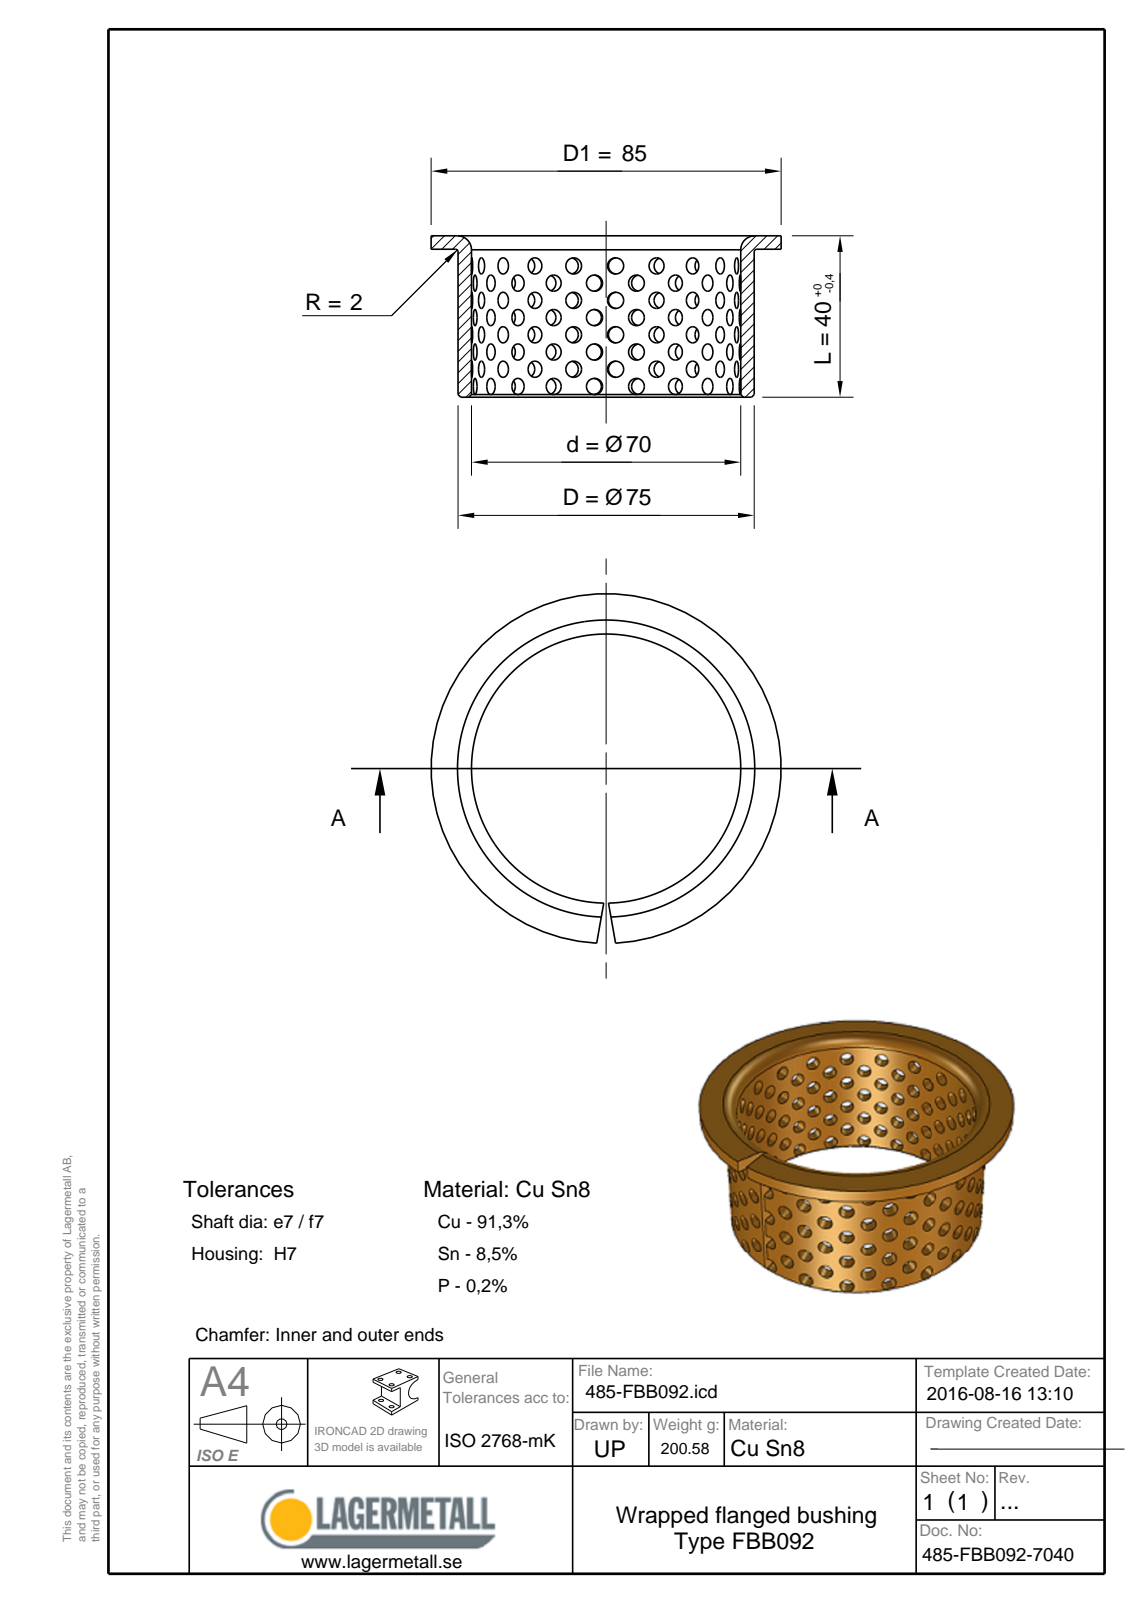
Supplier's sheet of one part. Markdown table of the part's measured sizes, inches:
| quantity | value |
| --- | --- |
| part name | 485-FBB092-7040 |
| STEP written by | Spatial InterOp 3D (CONFIG_CONTROL_DESIGN) |
| units | inches |
| bodies | 1 solid, 12 faces (5 planar, 3 cylindrical, 4 other) |
| overall size | 3.346 × 3.345 × 1.575 |
| volume | 1.511 in³ |
| surface area | 32.83 in² |
| round holes (diameter × count) | 2.756 × 1 |
| round bosses / shafts (diameter × count) | 3.346 × 1, 2.953 × 1 |
| main face-to-face distances | 0.098, 1.476, 1.575 |
